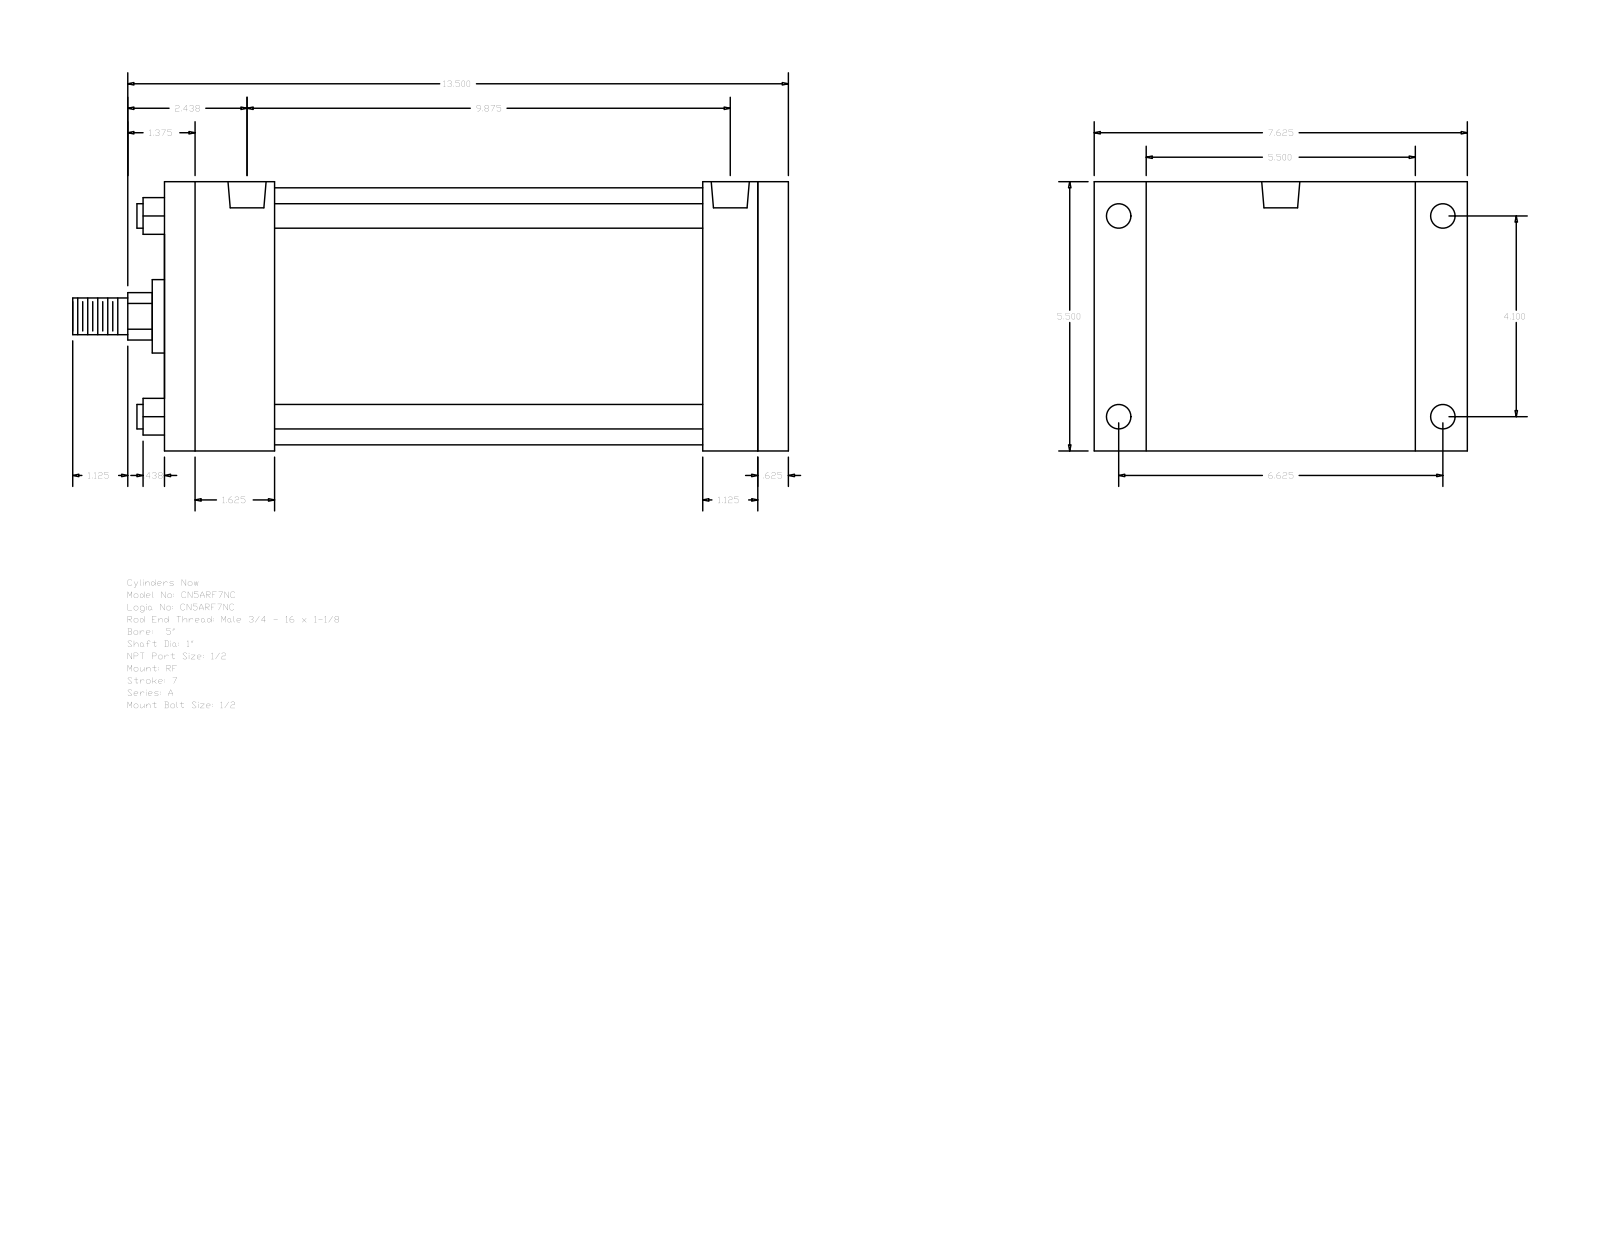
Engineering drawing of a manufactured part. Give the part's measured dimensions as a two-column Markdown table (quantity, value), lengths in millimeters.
| quantity | value |
| --- | --- |
| part name | A_RF__0500_1 |
| STEP written by | GSSL Pune (CONFIG_CONTROL_DESIGN) |
| units | millimeters |
| bodies | 0 solids, 92 faces (64 planar, 28 cylindrical, 0 other) |
| overall size | 371.48 × 193.68 × 139.7 |
| round holes (diameter × count) | 8.73 × 4, 12.7 × 4, 19.77 × 2 |
| round bosses / shafts (diameter × count) | 12.7 × 4, 133.35 × 1, 38.1 × 1, 25.4 × 1, 19.05 × 1 |
| partial cylindrical surfaces (radius × count) | 12.29 × 1 |
| main face-to-face distances | 139.7, 323.85, 307.97, 15.88, 28.57, 57.15, 250.82, 266.7, 279.4, 222.25 |
| hole center spacings | 2.39, 104.14, 168.28, 197.9, 246.05, 248.44, 250.83 |
